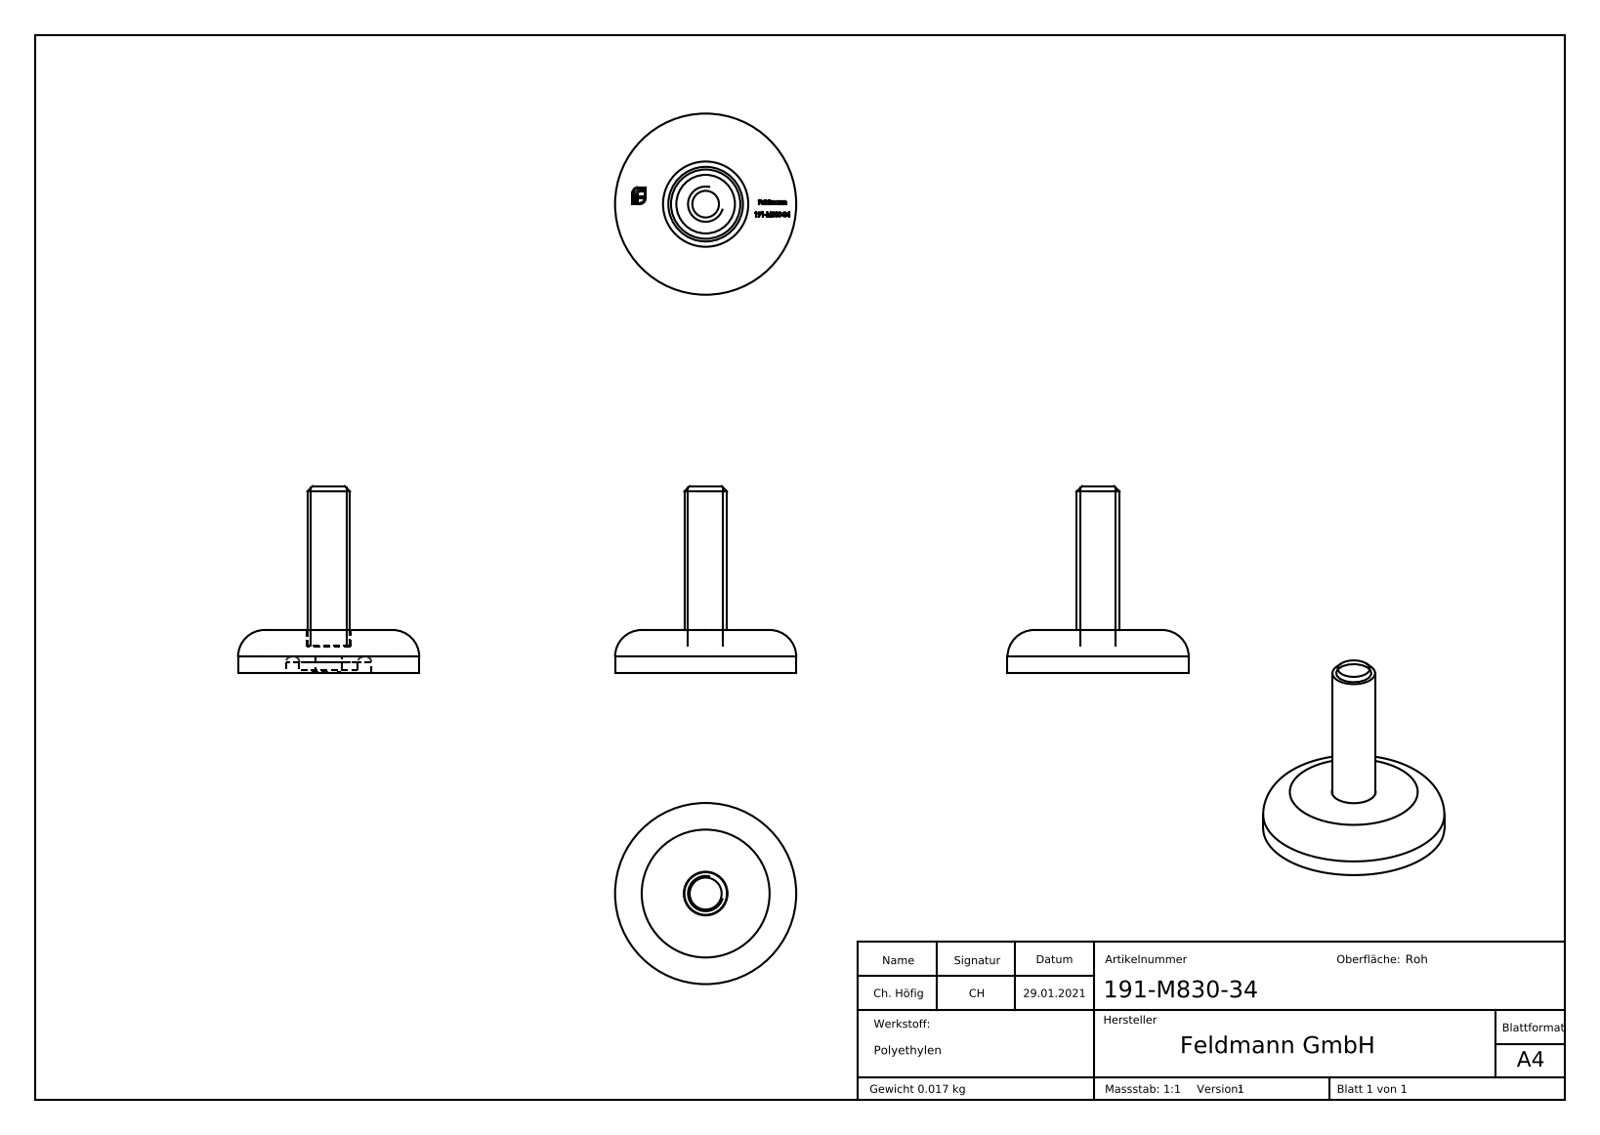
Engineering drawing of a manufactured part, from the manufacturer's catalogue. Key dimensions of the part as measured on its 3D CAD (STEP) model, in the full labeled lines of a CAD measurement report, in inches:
Part name (STEP PRODUCT): 191-M830-34
STEP written by: SolidWorks 2018 (CONFIG_CONTROL_DESIGN)
Units: inches
Bodies: 2 solids, 316 faces (165 planar, 12 cylindrical, 139 other)
Overall size (bounding box): 1.378 × 1.339 × 1.339
Volume: 0.468 in³ · Surface area: 5.575 in²
Round holes (diameter × count): ⌀0.197 ×1, ⌀0.323 ×1, ⌀0.63 ×1
Round bosses / shafts (diameter × count): ⌀1.339 ×1, ⌀0.433 ×1, ⌀0.315 ×1
Main face-to-face distances: 0.315, 0.197, 0.118, 0.02, 0.295, 0.193, 0.173, 0.122, 0.177, 0.075
